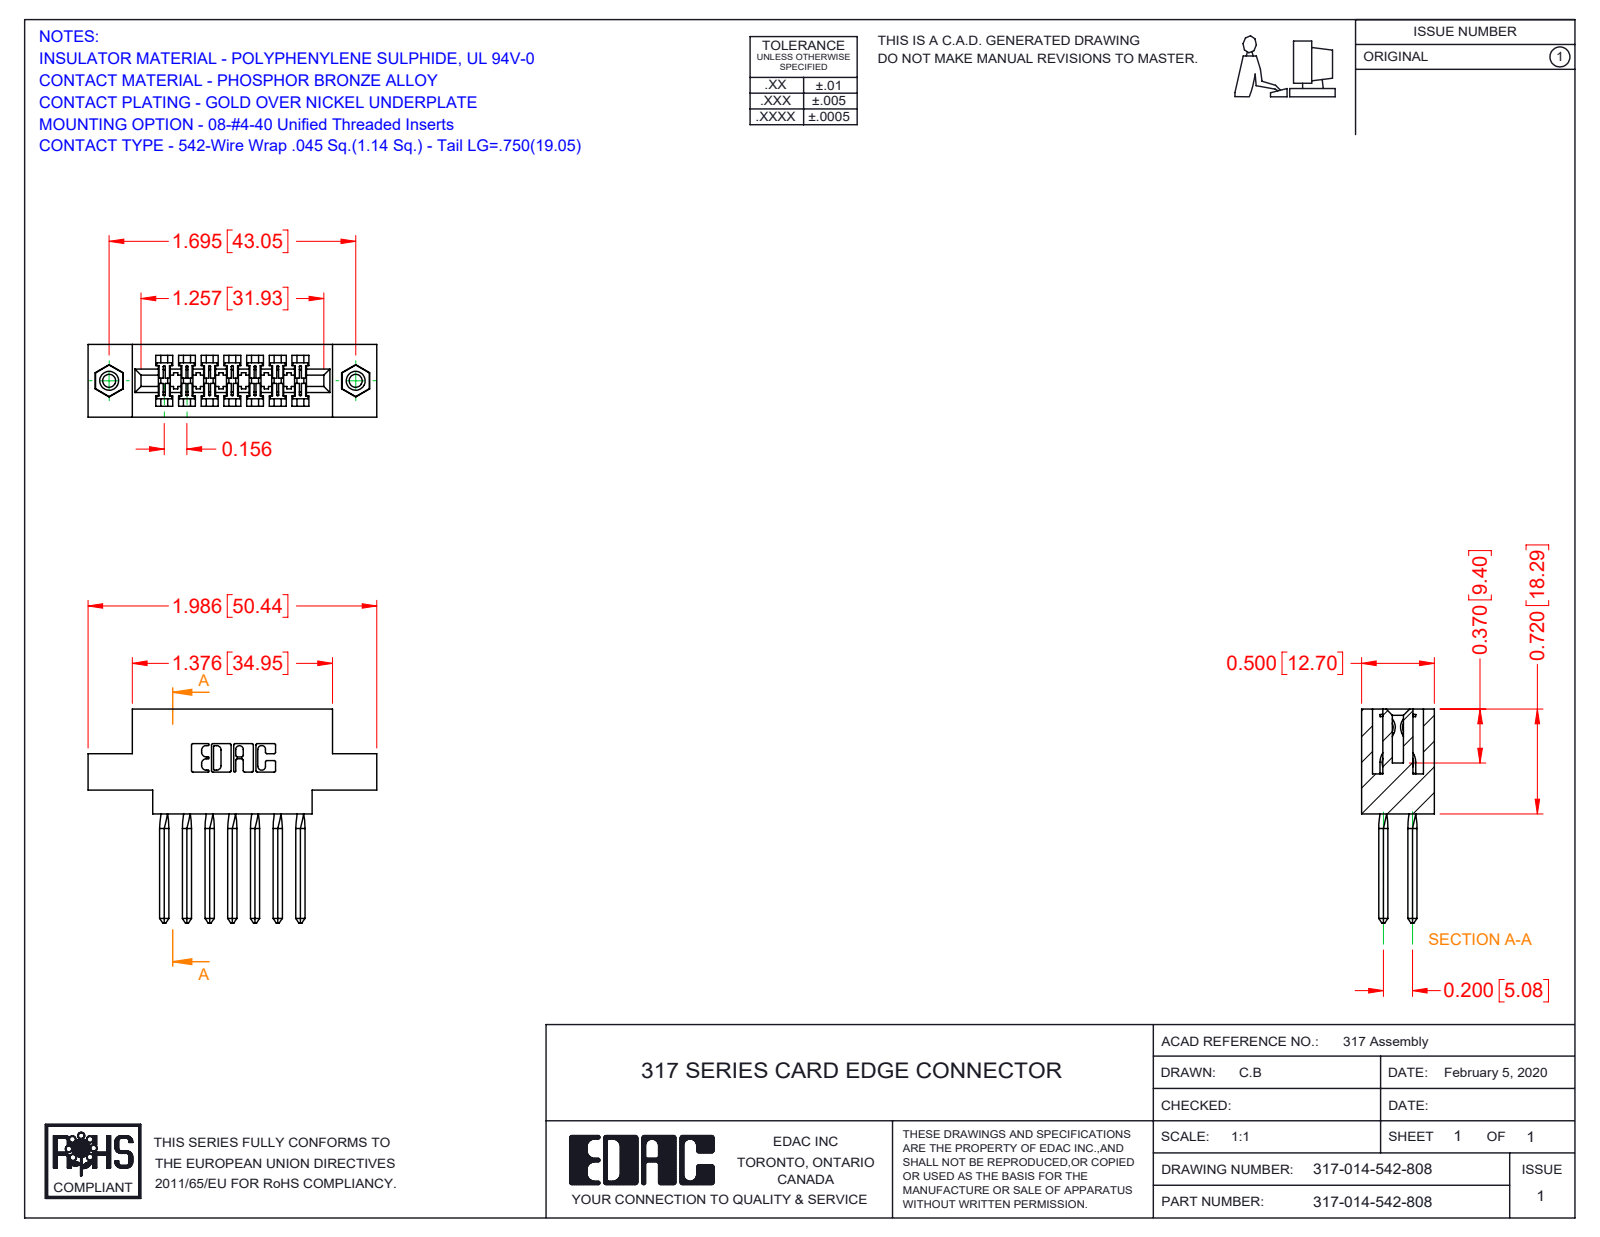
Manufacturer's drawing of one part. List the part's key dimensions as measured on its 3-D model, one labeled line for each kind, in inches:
Part name (STEP PRODUCT): 317-014-542-808; 317-290-003_542; 317 Part_.156 Dia - TI; 345-250-001_345-250-003-102
STEP written by: SolidWorks 2016 (CONFIG_CONTROL_DESIGN)
Units: inches
Bodies: 17 solids, 960 faces (734 planar, 154 cylindrical, 72 other)
Overall size (bounding box): 1.986 × 1.47 × 0.5
Volume: 0.436 in³ · Surface area: 13.7 in²
Round holes (diameter × count): ⌀0.089 ×2, ⌀0.125 ×2, ⌀0.156 ×2
Round bosses / shafts (diameter × count): ⌀0.155 ×2
Partial cylindrical surfaces — rounded edges, fillets, slot ends (radius × count): R0.006 ×28, R0.01 ×22, R0.007 ×6, R0.031 ×6, R0.026 ×3, R0.074 ×2, R0.089 ×2, R0.1 ×2
Main face-to-face distances: 0.5, 0.11, 0.075, 0.425, 0.156, 0.116, 0.22, 0.065, 0.136, 0.163
Hole centre spacings: 1.695
